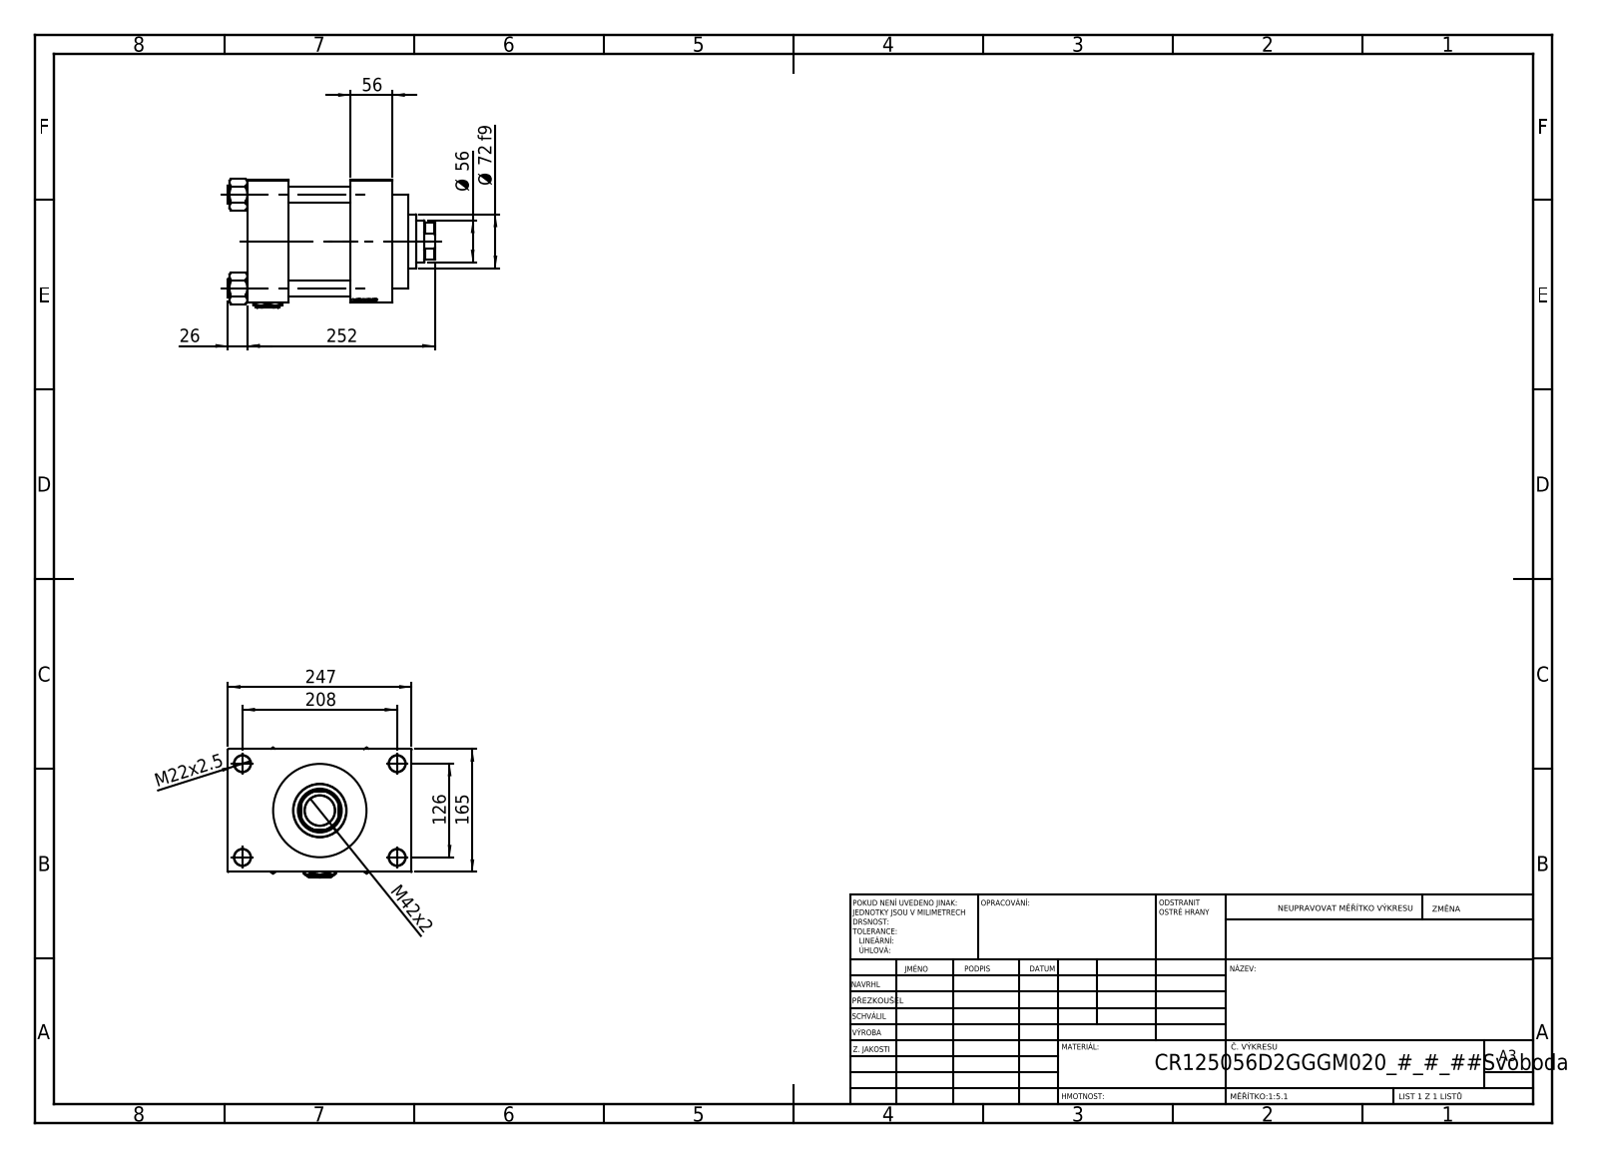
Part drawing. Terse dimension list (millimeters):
name: V215CR_VCP_D; V215CR_D_TYCINKA; V215CR_D_Body; V215_VC_A (+2 more)
written by: SolidWorks 2019 (CONFIG_CONTROL_DESIGN)
unit: mm
bodies: 12 solids, 1202 faces (568 planar, 94 cylindrical, 540 other)
size: 278 × 247 × 174.07
volume: 4 954 000 mm³; area: 535 785 mm²
holes: 8× ⌀22, 2× ⌀7, 2× ⌀32.24, 2× ⌀45, 1× ⌀40.5, 1× ⌀56, 1× ⌀59, 1× ⌀96, 1× ⌀125, 1× ⌀125.5
bosses: 4× ⌀25, 1× ⌀131, 1× ⌀72
rounds: 1× R27
face distances: 165, 84, 55, 139, 56, 195, 140, 41, 206, 173.74
hole spacings: 41.05, 89.02, 121.59, 125.9, 132.47, 166.95, 209.13, 126
